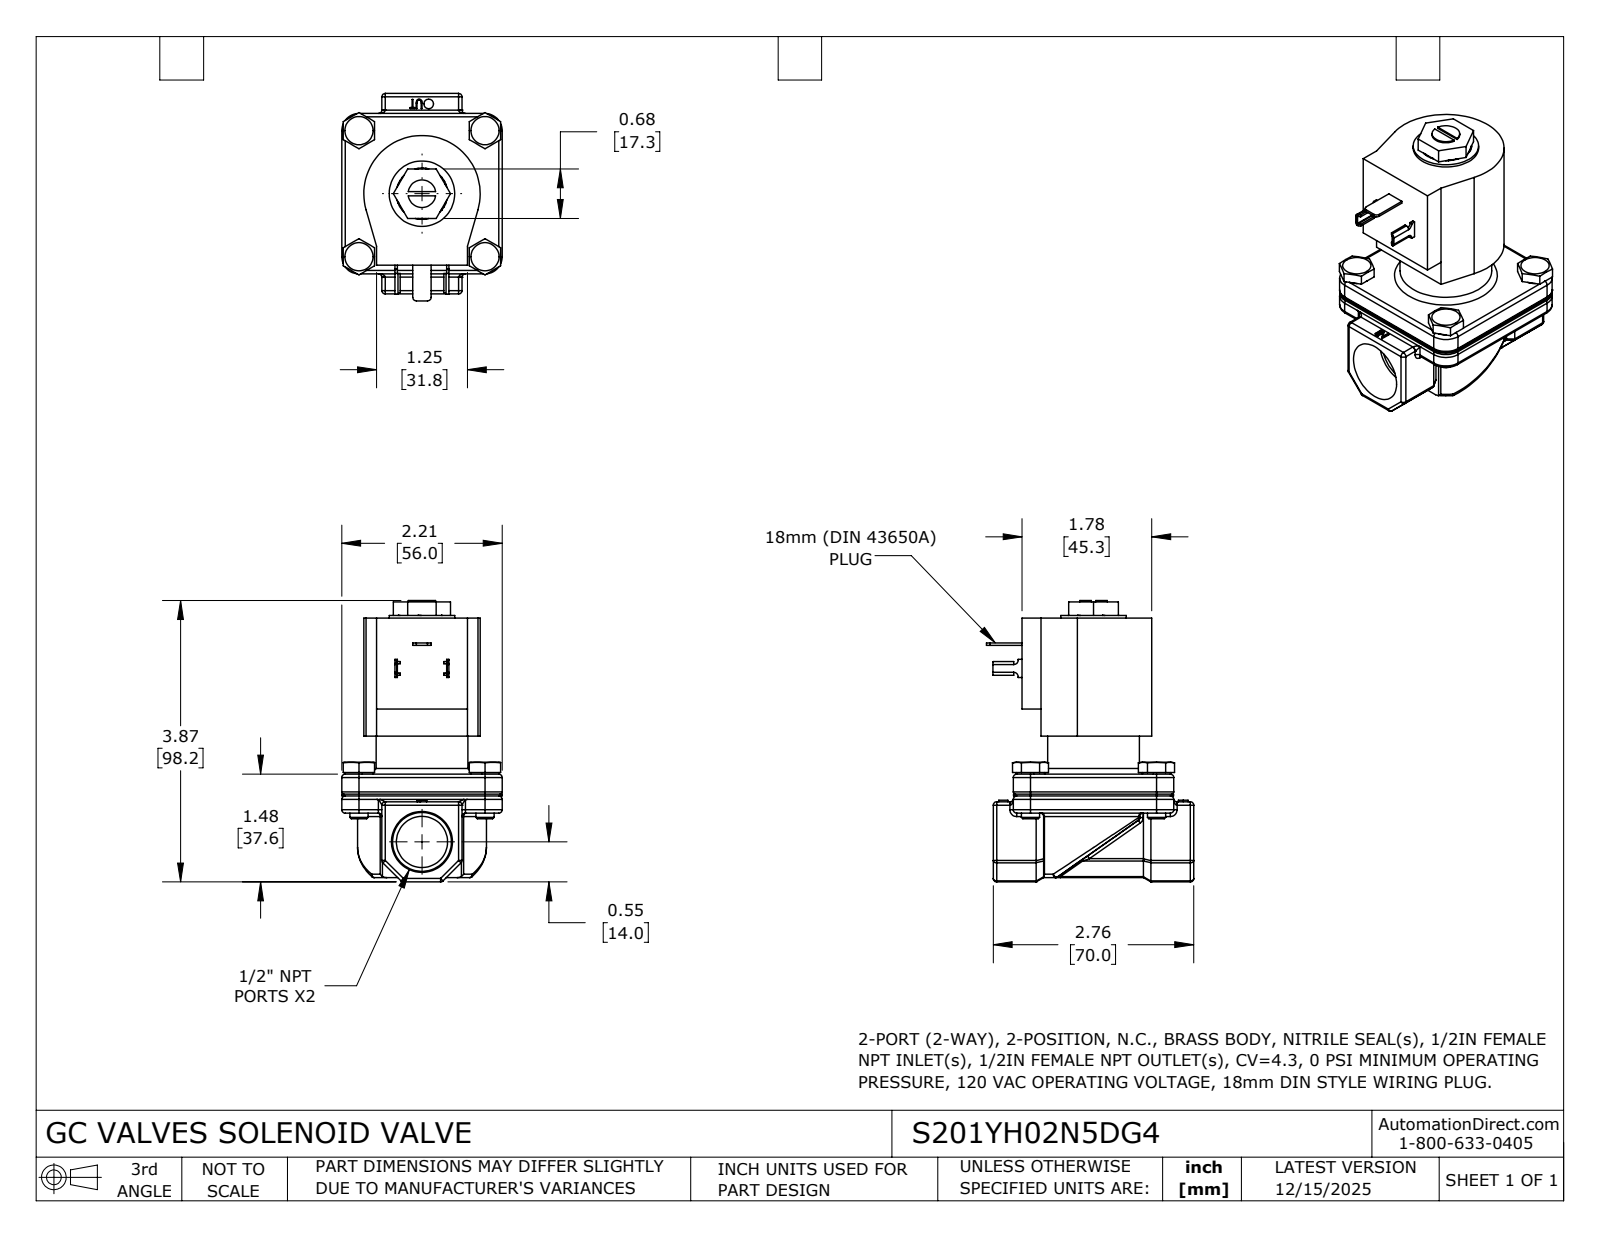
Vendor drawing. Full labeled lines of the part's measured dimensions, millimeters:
Part name (STEP PRODUCT): S201YH02N5DG4
STEP written by: SolidWorks 2024 (CONFIG_CONTROL_DESIGN)
Units: millimetres
Bodies: 1 solid, 507 faces (201 planar, 158 cylindrical, 148 other)
Overall size (bounding box): 98.2 × 72.4 × 56
Volume: 155 000 mm³ · Surface area: 27 540 mm²
Round holes (diameter × count): ⌀17.9 ×1, ⌀17.9 ×1
Round bosses / shafts (diameter × count): ⌀9.9 ×4, ⌀6.4 ×4, ⌀32 ×1, ⌀22.9 ×1, ⌀11.8 ×1, ⌀9.7 ×1
Partial cylindrical surfaces — rounded edges, fillets, slot ends (radius × count): R1.2 ×64, R0.2 ×4, R0.8 ×4, R1 ×4, R5.9 ×4, R6 ×4, R1.3 ×2, R1.5 ×2
Main face-to-face distances: 54.4, 1.5, 14, 42, 13.6, 68.1, 56, 7, 63, 26.9
